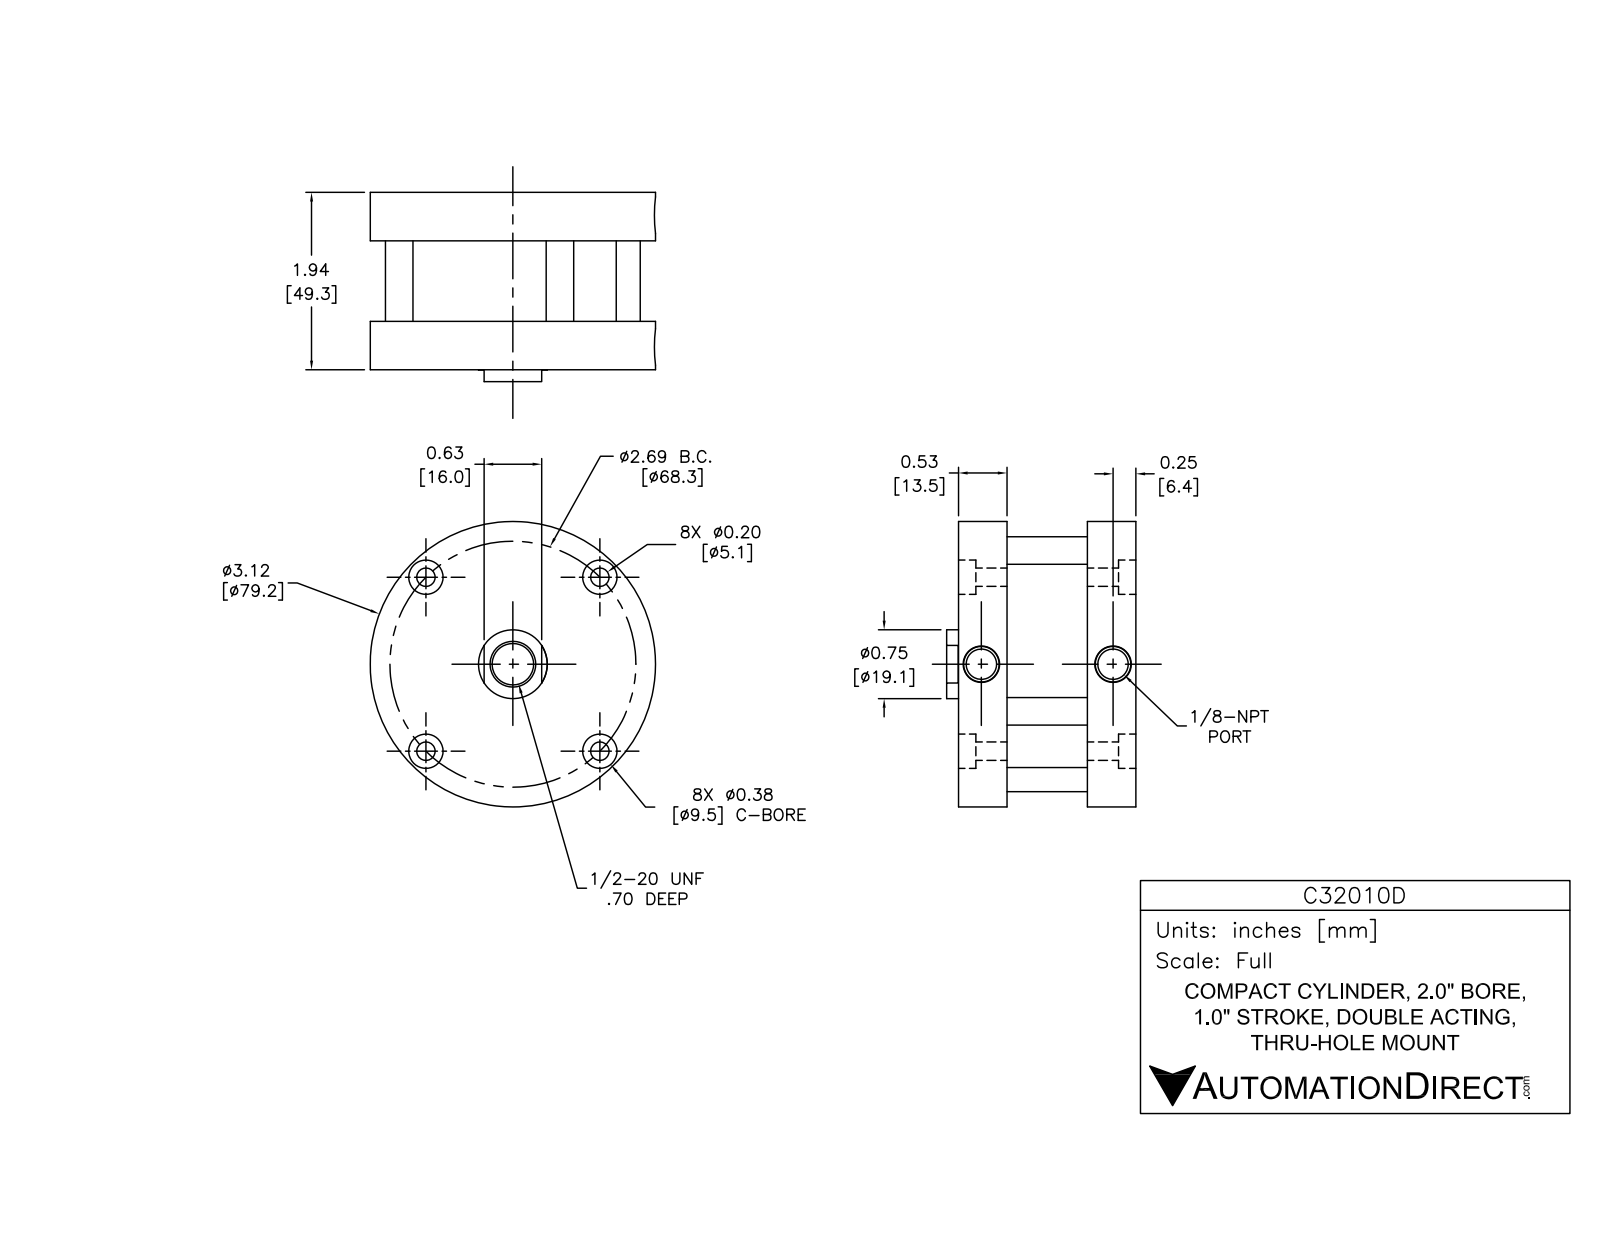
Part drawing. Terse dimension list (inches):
name: C32010D-FO1_BM_r; C32010D-FO1_BM_rod; C32010D-rod_part; C32010D (+3 more)
written by: SolidWorks 2014 (AUTOMOTIVE_DESIGN)
unit: in
bodies: 9 solids, 165 faces (49 planar, 98 cylindrical, 18 other)
size: 3.12 × 3.12 × 2.07
volume: 8.392 in³; area: 88.45 in²
holes: 4× ⌀0.2, 4× ⌀0.218, 4× ⌀0.343, 2× ⌀0.125, 1× ⌀0.446, 1× ⌀0.75, 1× ⌀0.752, 1× ⌀2, 1× ⌀2.06
bosses: 4× ⌀0.4, 1× ⌀3.12
face distances: 1.13, 0.25, 0.28, 1.94, 1.66, 1.41, 1.41, 0.53, 0.53, 0.88
hole spacings: 0.432, 1.345, 1.345, 1.572, 1.902, 1.902, 2.183, 2.655
